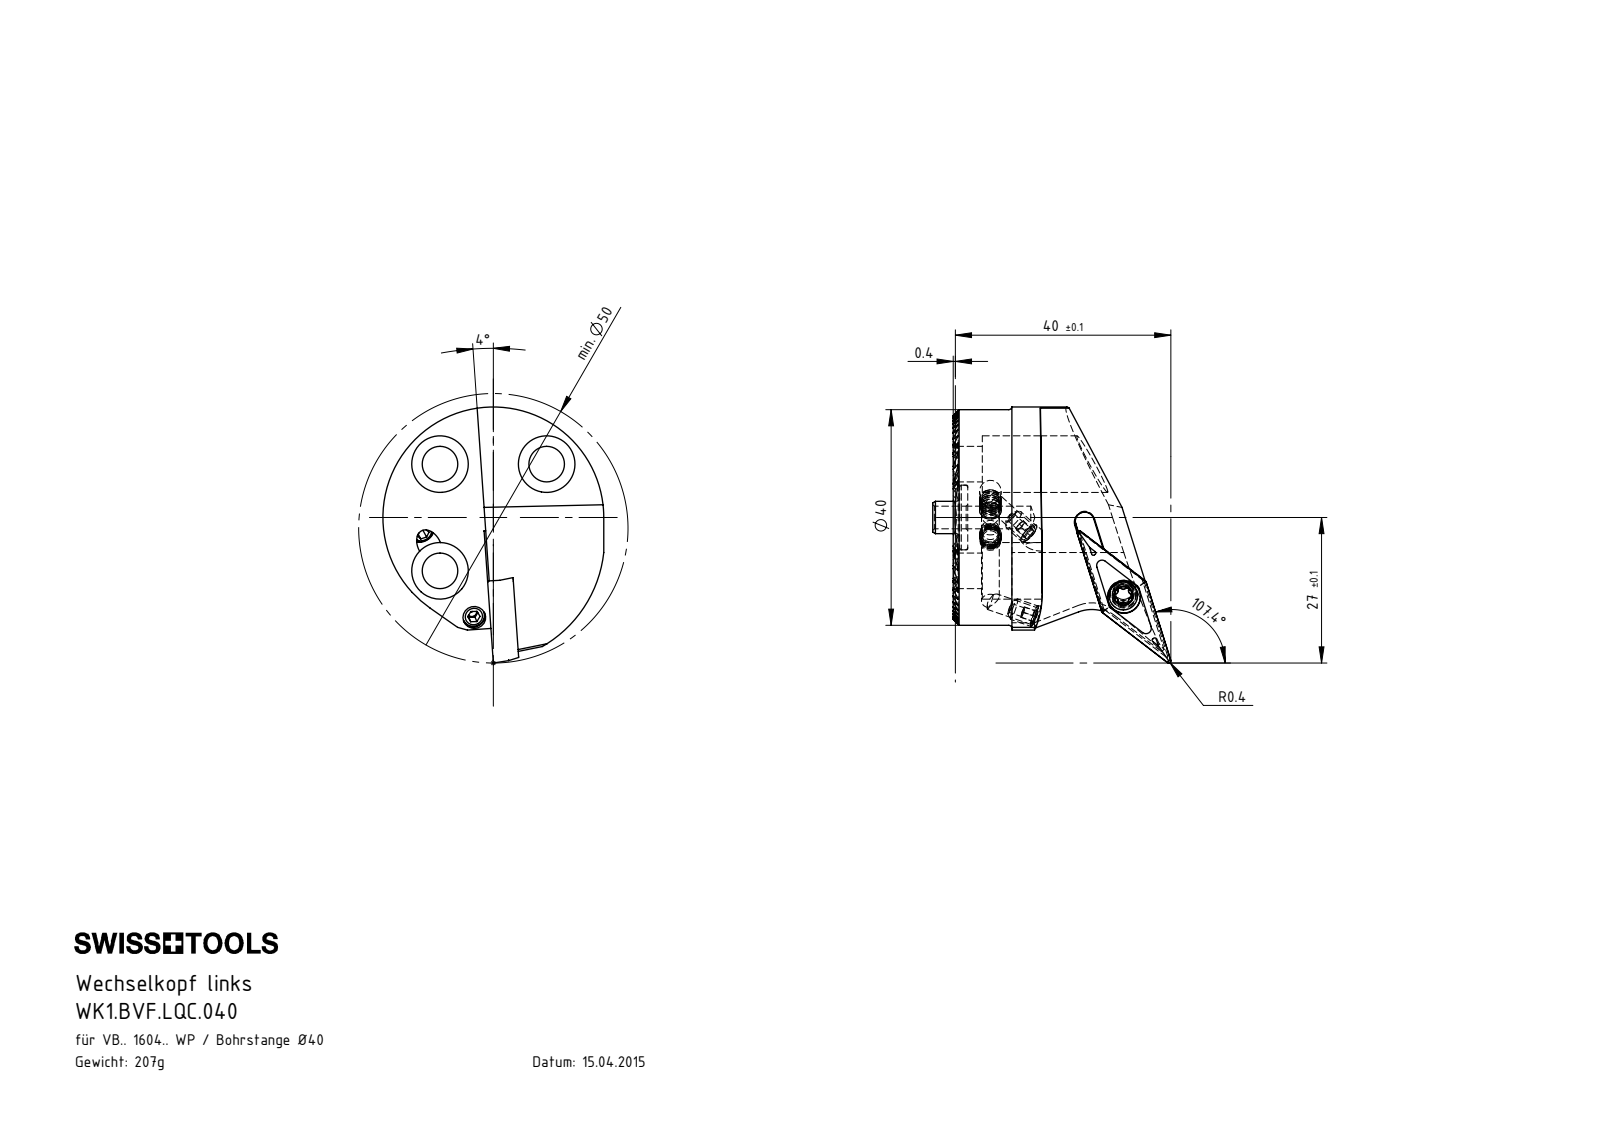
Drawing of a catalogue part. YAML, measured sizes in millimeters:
part_name: "WK1.BVF.LQC.040; WK2-ER1.001.012_A_Fertigbearbeitung; WKX-ER1.004.005_A_PreviewCfg; KVT_MB_600_040 (+3 more)"
step_written_by: "SolidWorks 2017 (AUTOMOTIVE_DESIGN)"
units: millimeters
bodies: {solids: 10, faces: 566, planar: 219, cylindrical: 199, other: 148}
overall_size: [47.5, 44.2, 41]
volume: 25912
surface_area: 11295
round_holes:
  - {diameter: 3.3, count: 5}
  - {diameter: 4.2, count: 3}
  - {diameter: 6.6, count: 3}
  - {diameter: 10.5, count: 3}
  - {diameter: 1.7, count: 2}
  - {diameter: 3, count: 2}
  - {diameter: 4, count: 1}
  - {diameter: 4.4, count: 1}
  - {diameter: 6.1, count: 1}
  - {diameter: 12, count: 1}
round_bosses_or_shafts:
  - {diameter: 4, count: 5}
  - {diameter: 40, count: 1}
  - {diameter: 6, count: 1}
  - {diameter: 5.25, count: 1}
partial_cylinders:
  - {radius: 0.12, count: 26}
  - {radius: 0.34, count: 6}
  - {radius: 0.59, count: 6}
  - {radius: 0.15, count: 2}
  - {radius: 1.75, count: 1}
  - {radius: 7, count: 1}
  - {radius: 20, count: 1}
  - {radius: 20.5, count: 1}
face_to_face_distances: [1.3, 2.6, 3.9, 12.99, 5.2, 11.69, 9.09, 10.39, 7.79, 6.5]
hole_center_spacings: [14, 19.8, 28]
